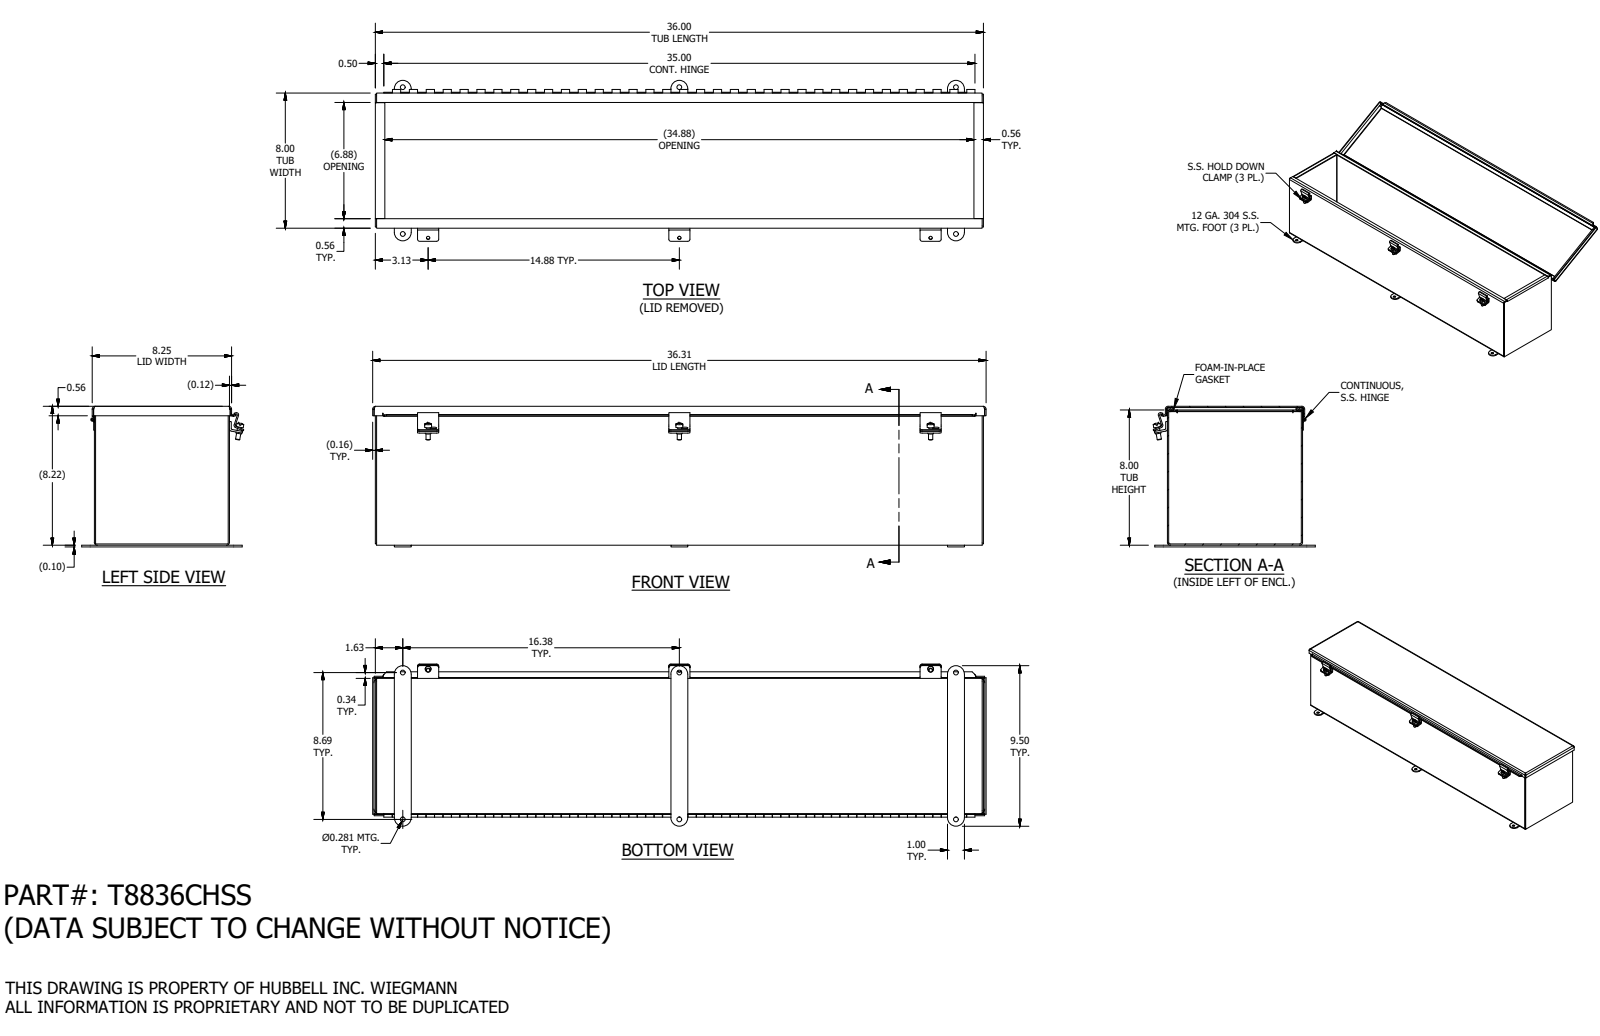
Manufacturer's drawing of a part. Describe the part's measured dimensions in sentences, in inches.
The part is named "T8836CHSS". Its 3-D file was written by "SolidWorks 2019 (AUTOMOTIVE_DESIGN)". It is 20 solids with 719 faces: 431 planar, 249 cylindrical and 39 other. Overall it measures 36.313 by 9.598 by 8.322 inches. Its volume is 114.6 cubic inches and its surface area 3 056 square inches. Round holes: 6 of diameter 0.11, 6 of diameter 0.281, 3 of diameter 0.196, 1 of diameter 0.116. Round bosses or shafts: 3 of diameter 0.41, 3 of diameter 0.344, 3 of diameter 0.25, 1 of diameter 0.2, 1 of diameter 0.1. Partial cylindrical surfaces (rounded edges, fillets, slot ends): 12 of radius 0.125, 11 of radius 0.094, 11 of radius 0.168, 8 of radius 0.085, 6 of radius 0.133, 6 of radius 0.5, 4 of radius 0.242, 3 of radius 0.063. The main face-to-face distances are 0.074, 7.926, 8.144, 8, 7.852, 8.218, 8.07, 35.926, 0.218, 35.852. The hole center spacings are 14.875, 16.375, 18.537, 0.75, 8.687, 14.875, 29.75, 32.75.
